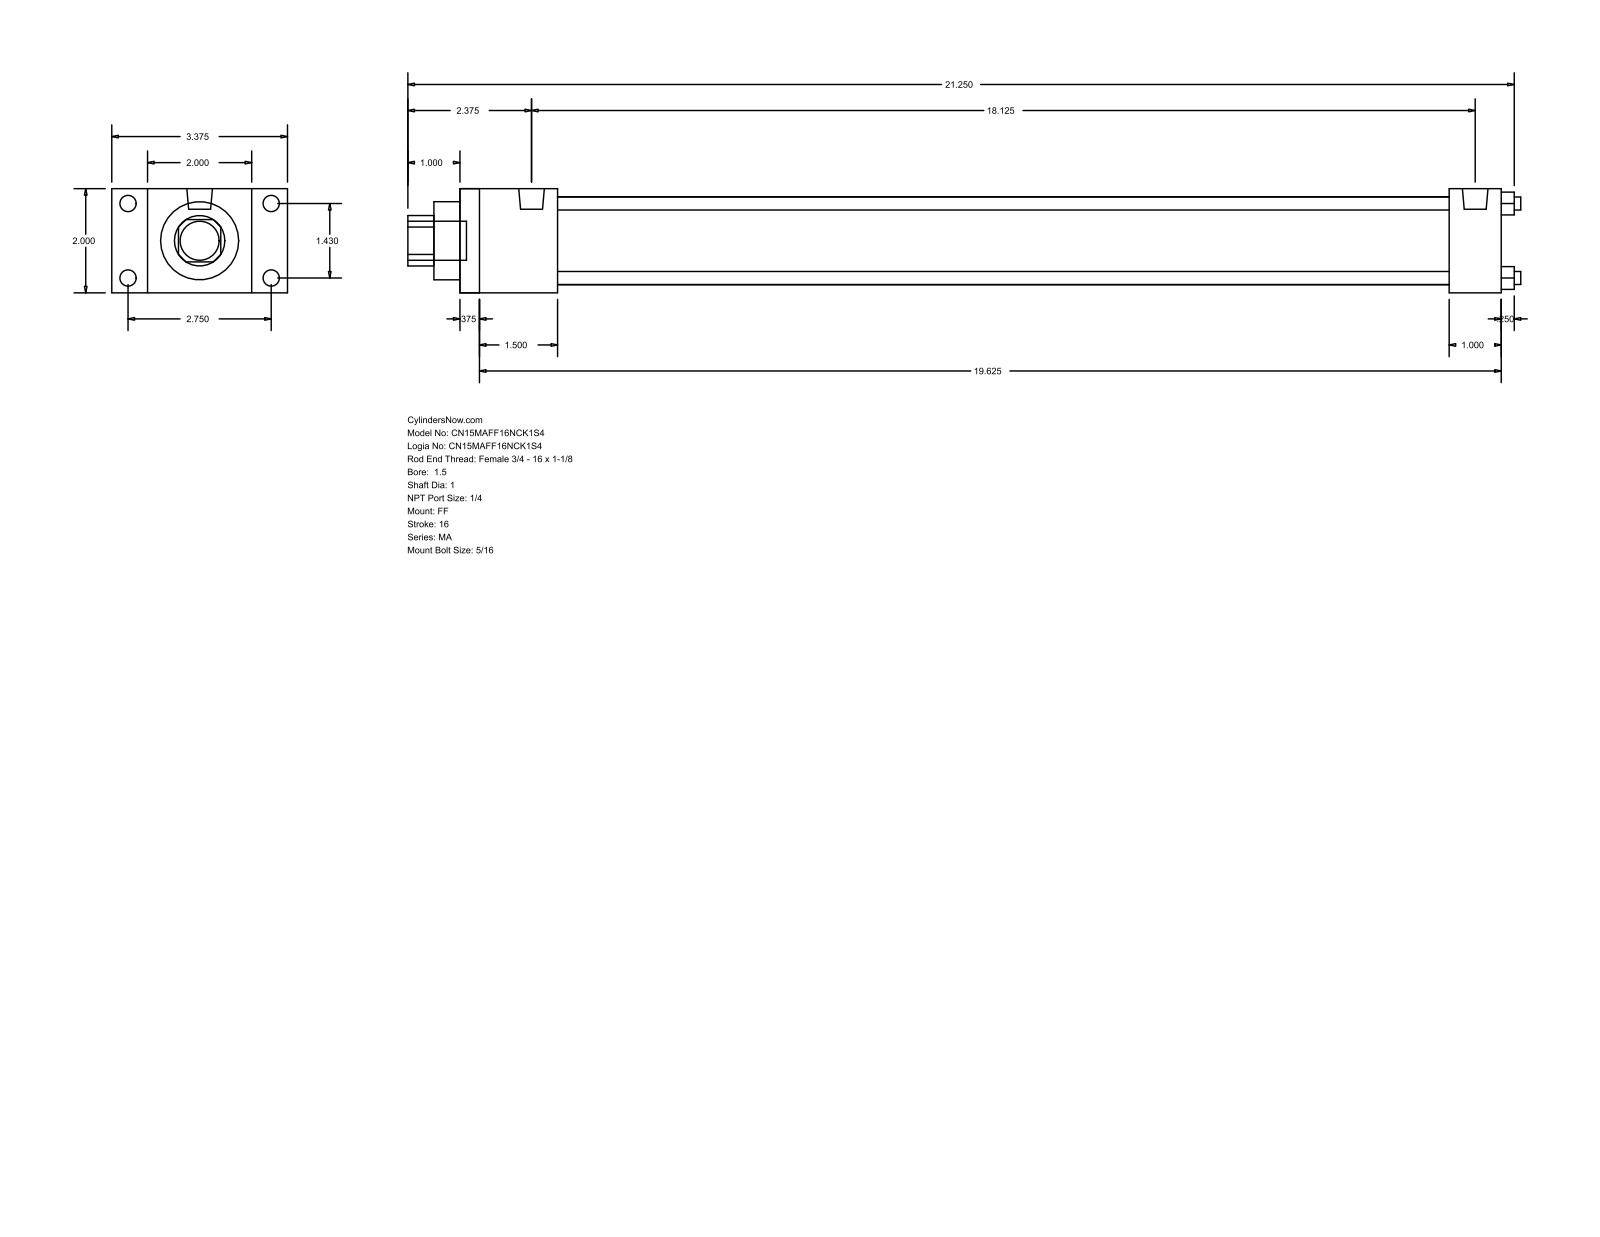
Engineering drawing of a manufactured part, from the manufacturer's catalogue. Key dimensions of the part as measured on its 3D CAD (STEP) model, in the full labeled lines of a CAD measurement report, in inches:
Part name (STEP PRODUCT): MA_FF__0150_1
STEP written by: GSSL Pune (CONFIG_CONTROL_DESIGN)
Units: inches
Bodies: 0 solids, 92 faces (64 planar, 28 cylindrical, 0 other)
Overall size (bounding box): 21.375 × 3.375 × 2
Round holes (diameter × count): ⌀0.25 ×4, ⌀1 ×1, ⌀1.5 ×1, ⌀1.69 ×1
Round bosses / shafts (diameter × count): ⌀0.313 ×8, ⌀0.492 ×2, ⌀0.75 ×1
Partial cylindrical surfaces — rounded edges, fillets, slot ends (radius × count): R0.484 ×1
Main face-to-face distances: 2, 20, 0.375, 19.625, 1, 1.875, 19, 1.5, 18.625, 17.125
Hole centre spacings: 1.011, 1.43, 2.022
